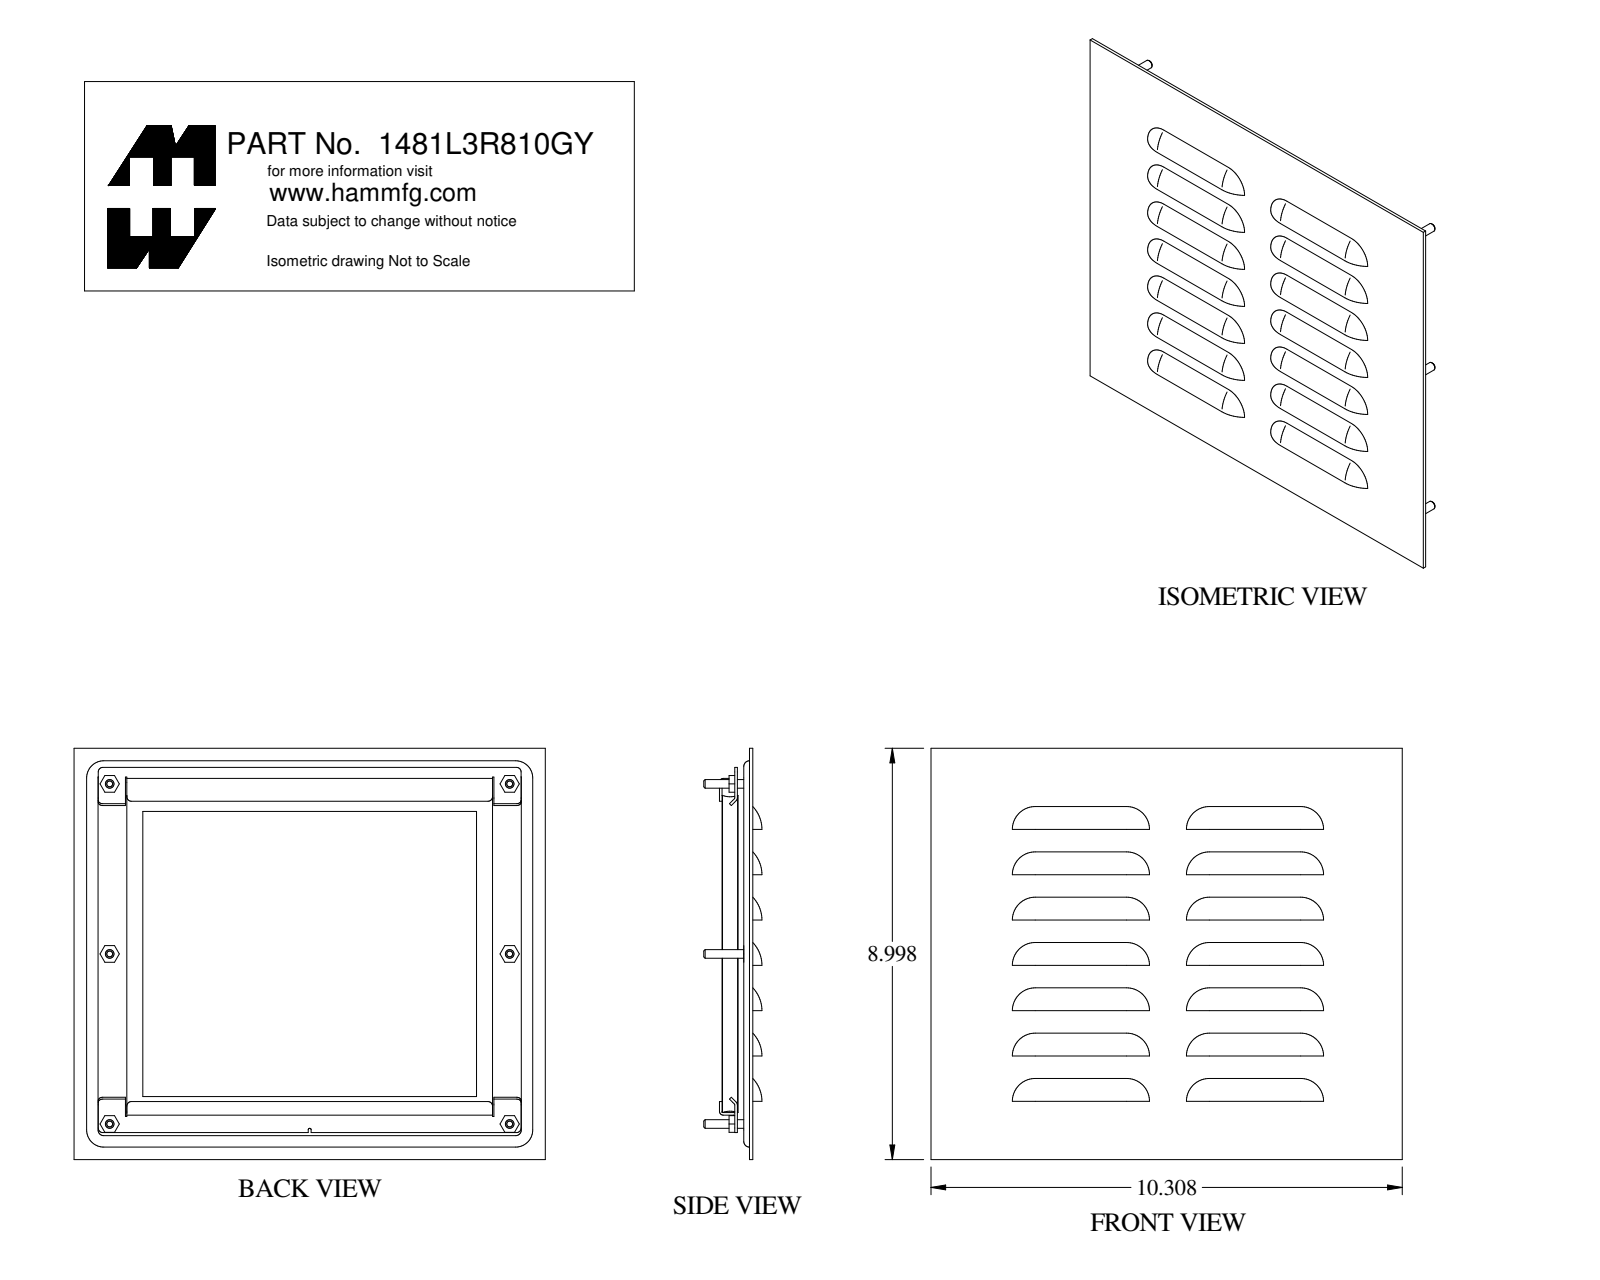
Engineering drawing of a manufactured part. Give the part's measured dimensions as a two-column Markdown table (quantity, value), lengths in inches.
| quantity | value |
| --- | --- |
| part name | 1481L3R810GY |
| STEP written by | SolidWorks 2021 (AUTOMOTIVE_DESIGN) |
| units | inches |
| bodies | 17 solids, 384 faces (185 planar, 119 cylindrical, 80 other) |
| overall size | 10.308 × 8.998 × 1.272 |
| volume | 23.59 in³ |
| surface area | 408 in² |
| round holes (diameter × count) | 0.156 × 6, 0.22 × 4 |
| round bosses / shafts (diameter × count) | 0.25 × 6, 0.188 × 6 |
| partial cylindrical surfaces (radius × count) | 0.1 × 12, 0.653 × 7, 0.725 × 7, 0.029 × 6, 0.086 × 6, 0.125 × 4, 0.126 × 4, 0.374 × 4 |
| main face-to-face distances | 0.072, 0.3, 0.25, 0.372, 0.622, 0.55, 0.05, 0.322, 0.6, 0.672 |
| hole center spacings | 3.72, 7.44, 9.507, 11.485, 8.75, 8.75, 9.508 |
